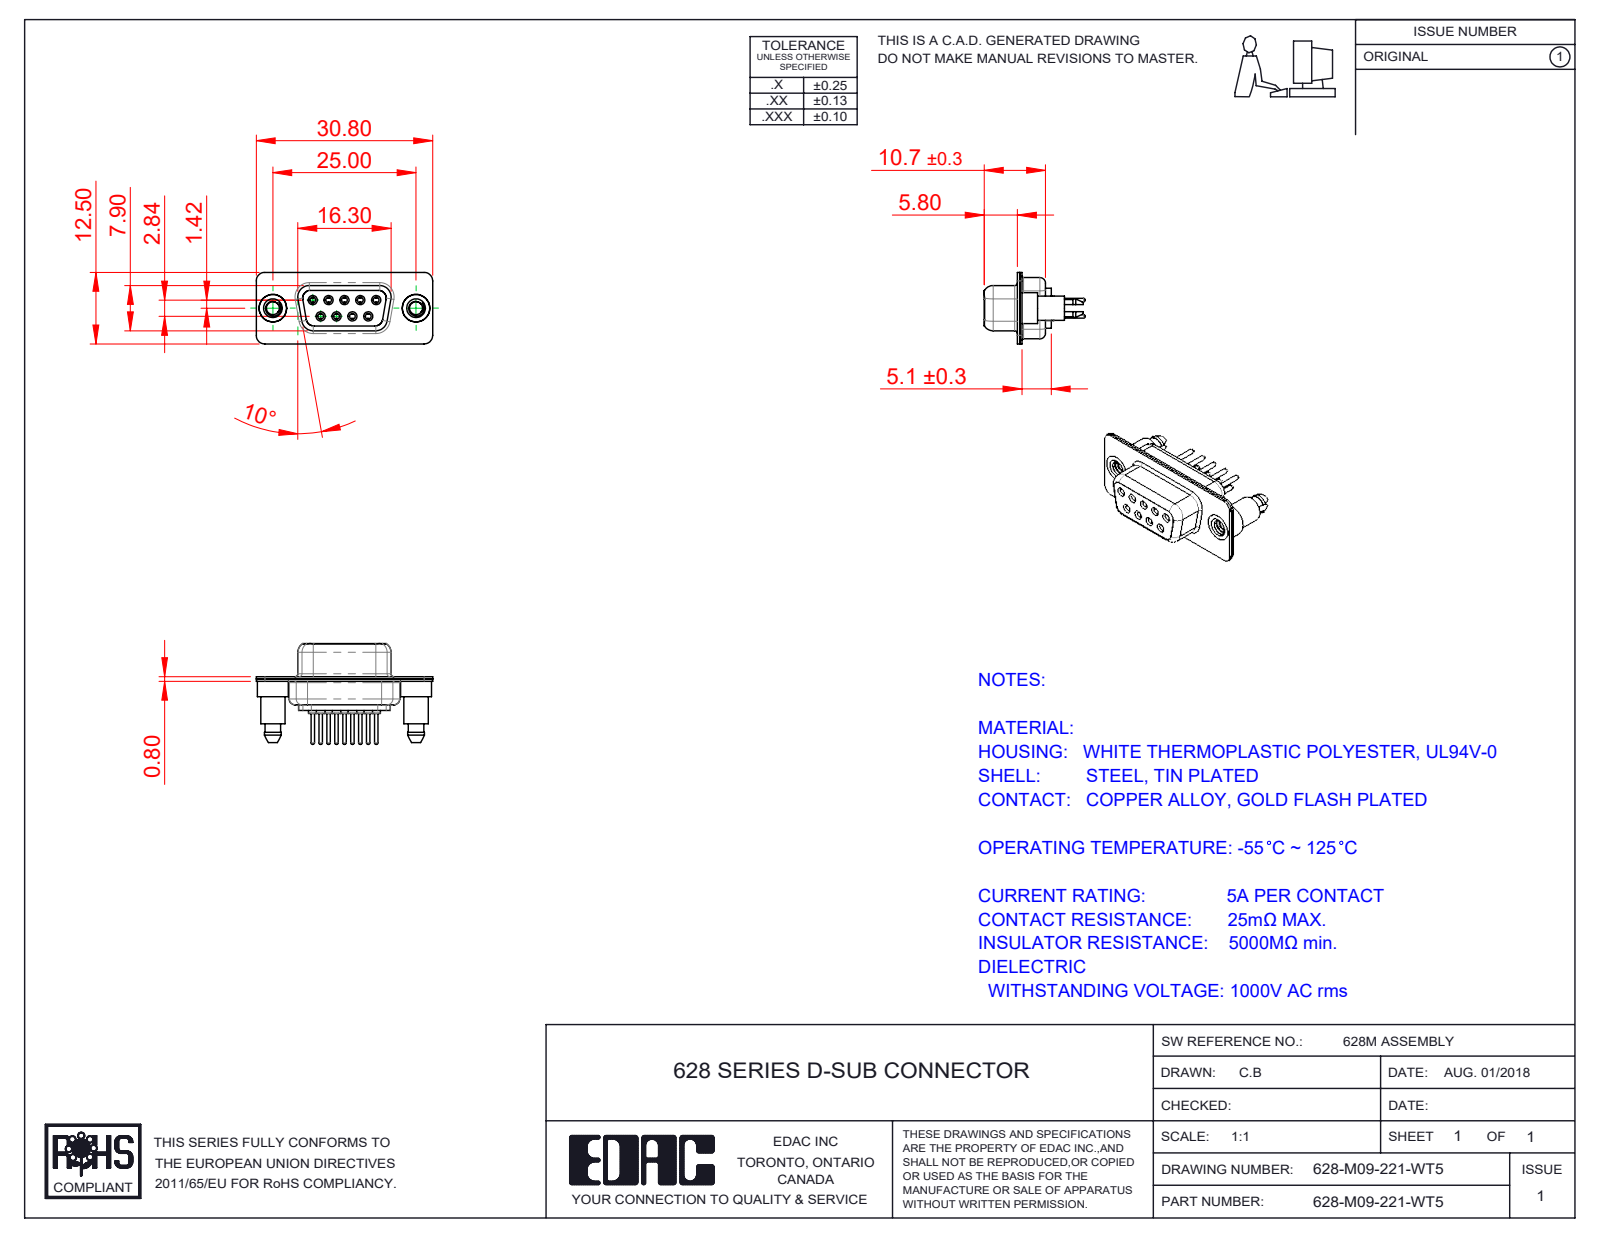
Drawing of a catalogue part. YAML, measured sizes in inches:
part_name: "628M Housing_09 Contacts; 628M Shell Rear_09 Contacts; 628M Contact Row 2_21; 628M Contact Row 1_21 (+3 more)"
step_written_by: "SolidWorks 2020 (CONFIG_CONTROL_DESIGN)"
units: inches
bodies: {solids: 14, faces: 824, planar: 218, cylindrical: 340, other: 266}
overall_size: [1.213, 0.693, 0.492]
volume: 0.112
surface_area: 7.37
round_holes:
  - {diameter: 0.039, count: 9}
  - {diameter: 0.043, count: 9}
  - {diameter: 0.067, count: 9}
  - {diameter: 0.071, count: 9}
  - {diameter: 0.079, count: 9}
  - {diameter: 0.089, count: 2}
  - {diameter: 0.157, count: 2}
  - {diameter: 0.189, count: 2}
round_bosses_or_shafts:
  - {diameter: 0.087, count: 9}
  - {diameter: 0.063, count: 9}
  - {diameter: 0.059, count: 9}
  - {diameter: 0.024, count: 9}
  - {diameter: 0.213, count: 2}
  - {diameter: 0.193, count: 2}
  - {diameter: 0.167, count: 2}
partial_cylinders:
  - {radius: 0.059, count: 18}
  - {radius: 0.079, count: 12}
  - {radius: 0.063, count: 10}
  - {radius: 0.053, count: 8}
  - {radius: 0.01, count: 4}
  - {radius: 0.02, count: 4}
  - {radius: 0.024, count: 4}
  - {radius: 0.026, count: 4}
face_to_face_distances: [0.016, 0.055, 0.018, 0.333, 0.031, 0.071, 0.039, 0.35, 0.244, 0.278]
hole_center_spacings: [0.124, 0.109, 0.218, 0.198, 0.198, 0.327, 0.28, 0.294]
